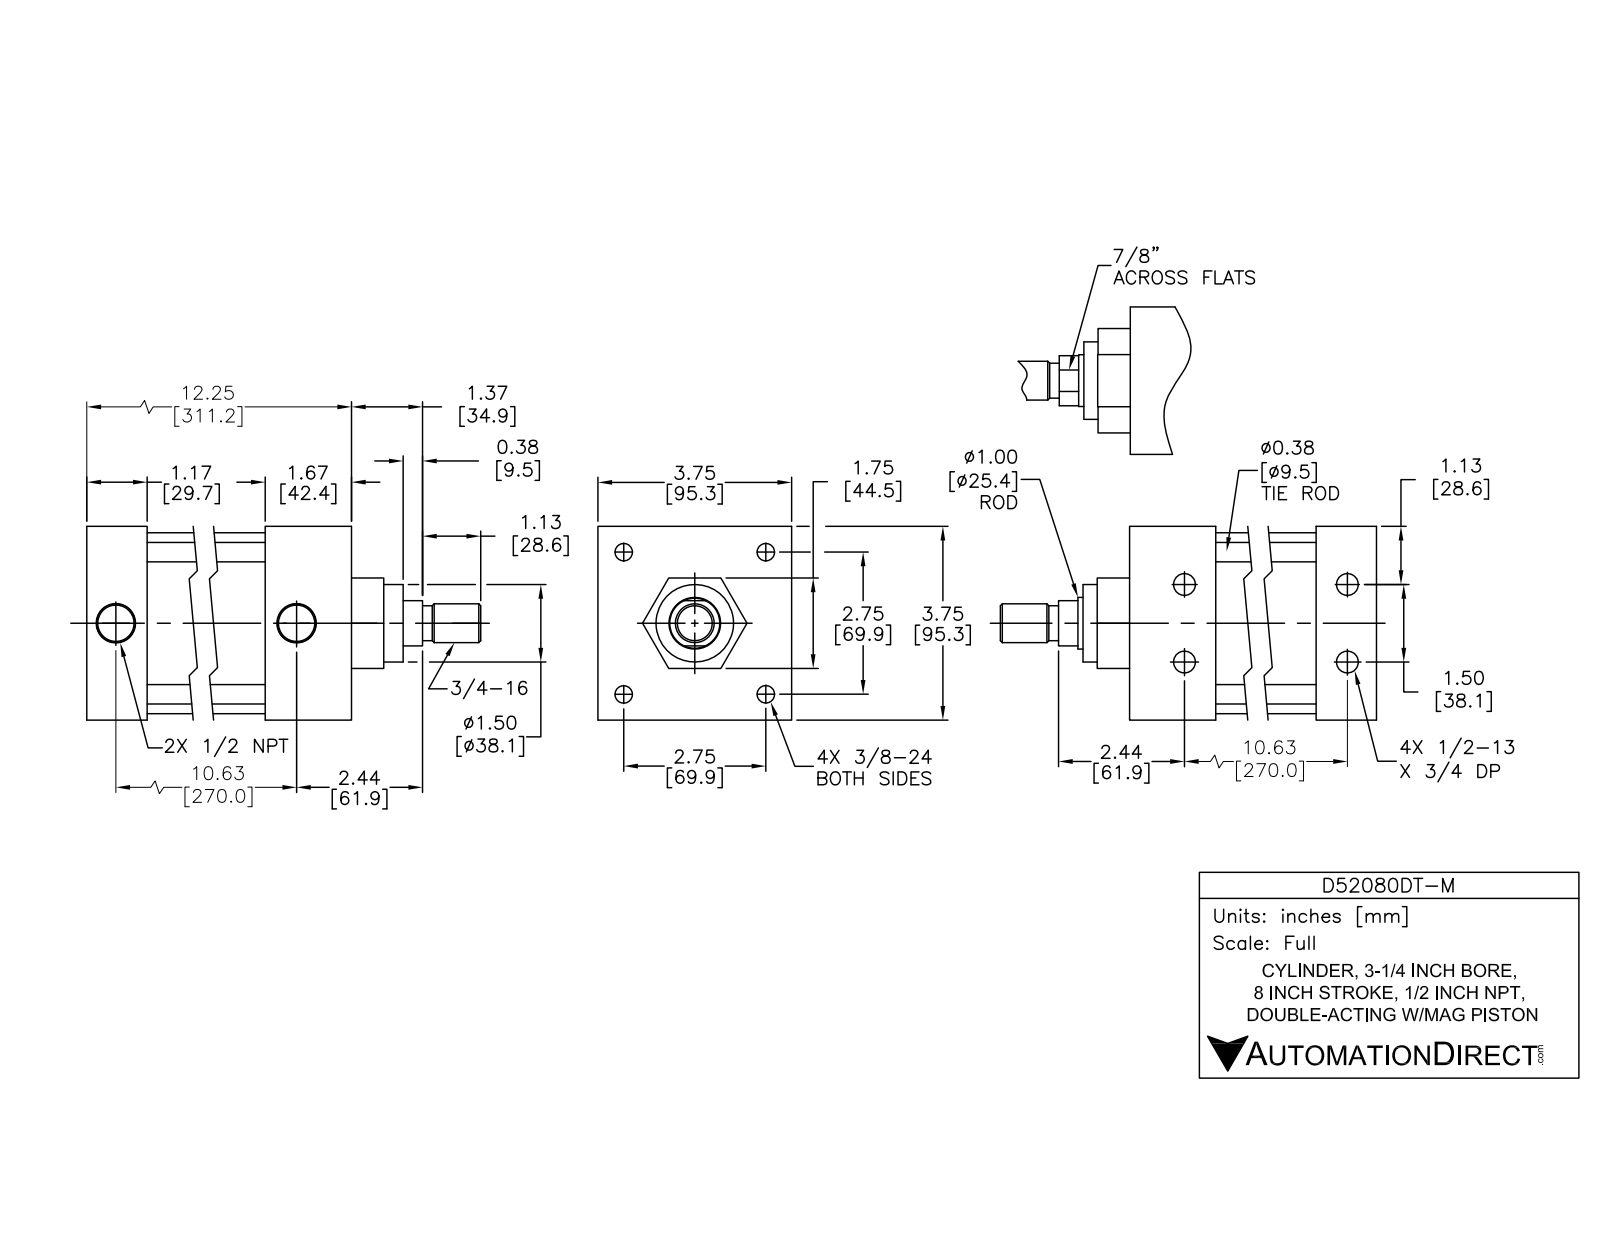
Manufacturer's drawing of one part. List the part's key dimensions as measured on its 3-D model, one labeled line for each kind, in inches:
Part name (STEP PRODUCT): D52080DT-M BODY; D52080DT-M PISTON; D52080DT-M
STEP written by: SolidWorks 2015 (AUTOMOTIVE_DESIGN)
Units: inches
Bodies: 12 solids, 303 faces (99 planar, 114 cylindrical, 90 other)
Overall size (bounding box): 14.745 × 3.75 × 3.75
Volume: 73.58 in³ · Surface area: 466 in²
Round holes (diameter × count): ⌀0.33 ×4, ⌀0.406 ×4, ⌀0.417 ×4, ⌀0.625 ×4, ⌀0.5 ×2, ⌀0.766 ×2, ⌀1 ×1, ⌀1.003 ×1, ⌀3.25 ×1
Round bosses / shafts (diameter × count): ⌀0.609 ×4, ⌀0.375 ×4, ⌀0.34 ×4, ⌀3.5 ×1, ⌀3.247 ×1, ⌀1.75 ×1, ⌀0.997 ×1, ⌀0.97 ×1
Partial cylindrical surfaces — rounded edges, fillets, slot ends (radius × count): R0.375 ×4
Main face-to-face distances: 3.75, 0.08, 9.326, 12.246, 1.75, 10.997, 1.249, 9.751, 1.246, 2.495
Hole centre spacings: 0.75, 0.76, 1.5, 1.95, 1.95, 2.758, 2.758, 3.9
